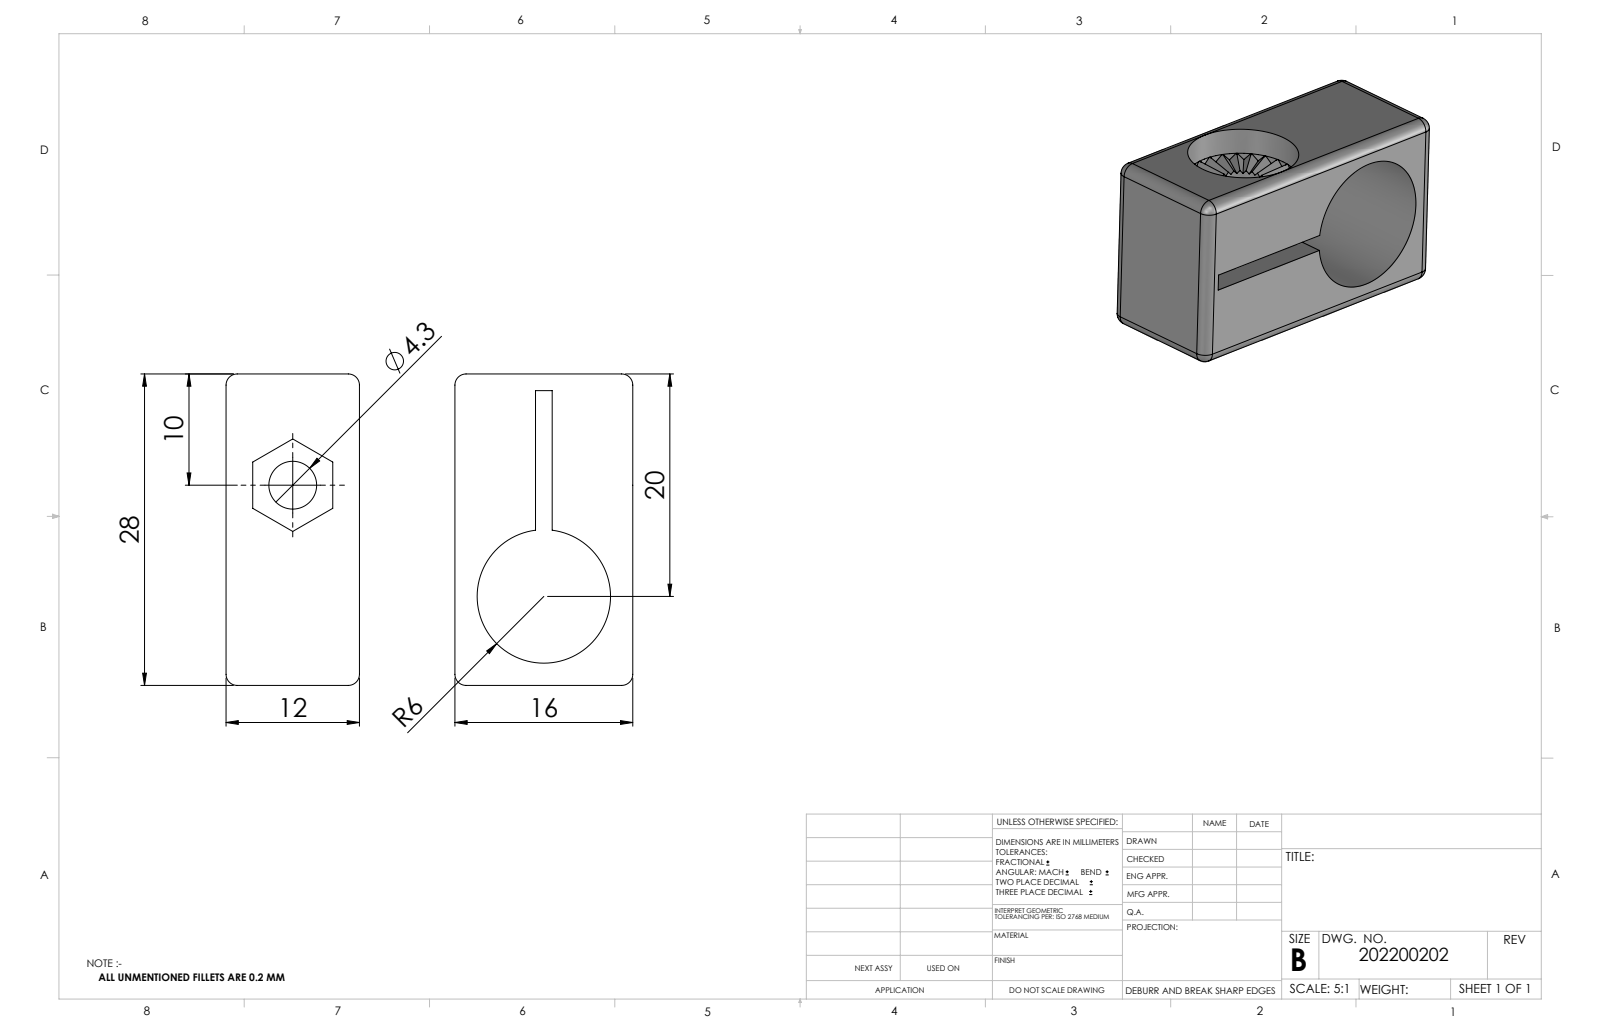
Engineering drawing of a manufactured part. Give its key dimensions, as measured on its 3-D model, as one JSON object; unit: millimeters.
{"part_name": "202200202_c_1", "step_written_by": "SolidWorks 2014 (CONFIG_CONTROL_DESIGN)", "units": "millimeters", "bodies": {"solids": 1, "faces": 189, "planar": 161, "cylindrical": 20, "other": 8}, "overall_size": [28, 16, 12], "volume_mm3": 3267, "surface_area_mm2": 2590, "round_holes": [[4.3, 1], [10, 1], [12, 1]], "partial_cylinders_radius": [[1, 12]], "face_to_face_distances": [7.25, 8.75, 12, 16, 1.5, 28, 7.2, 13, 5.75, 4.25]}
